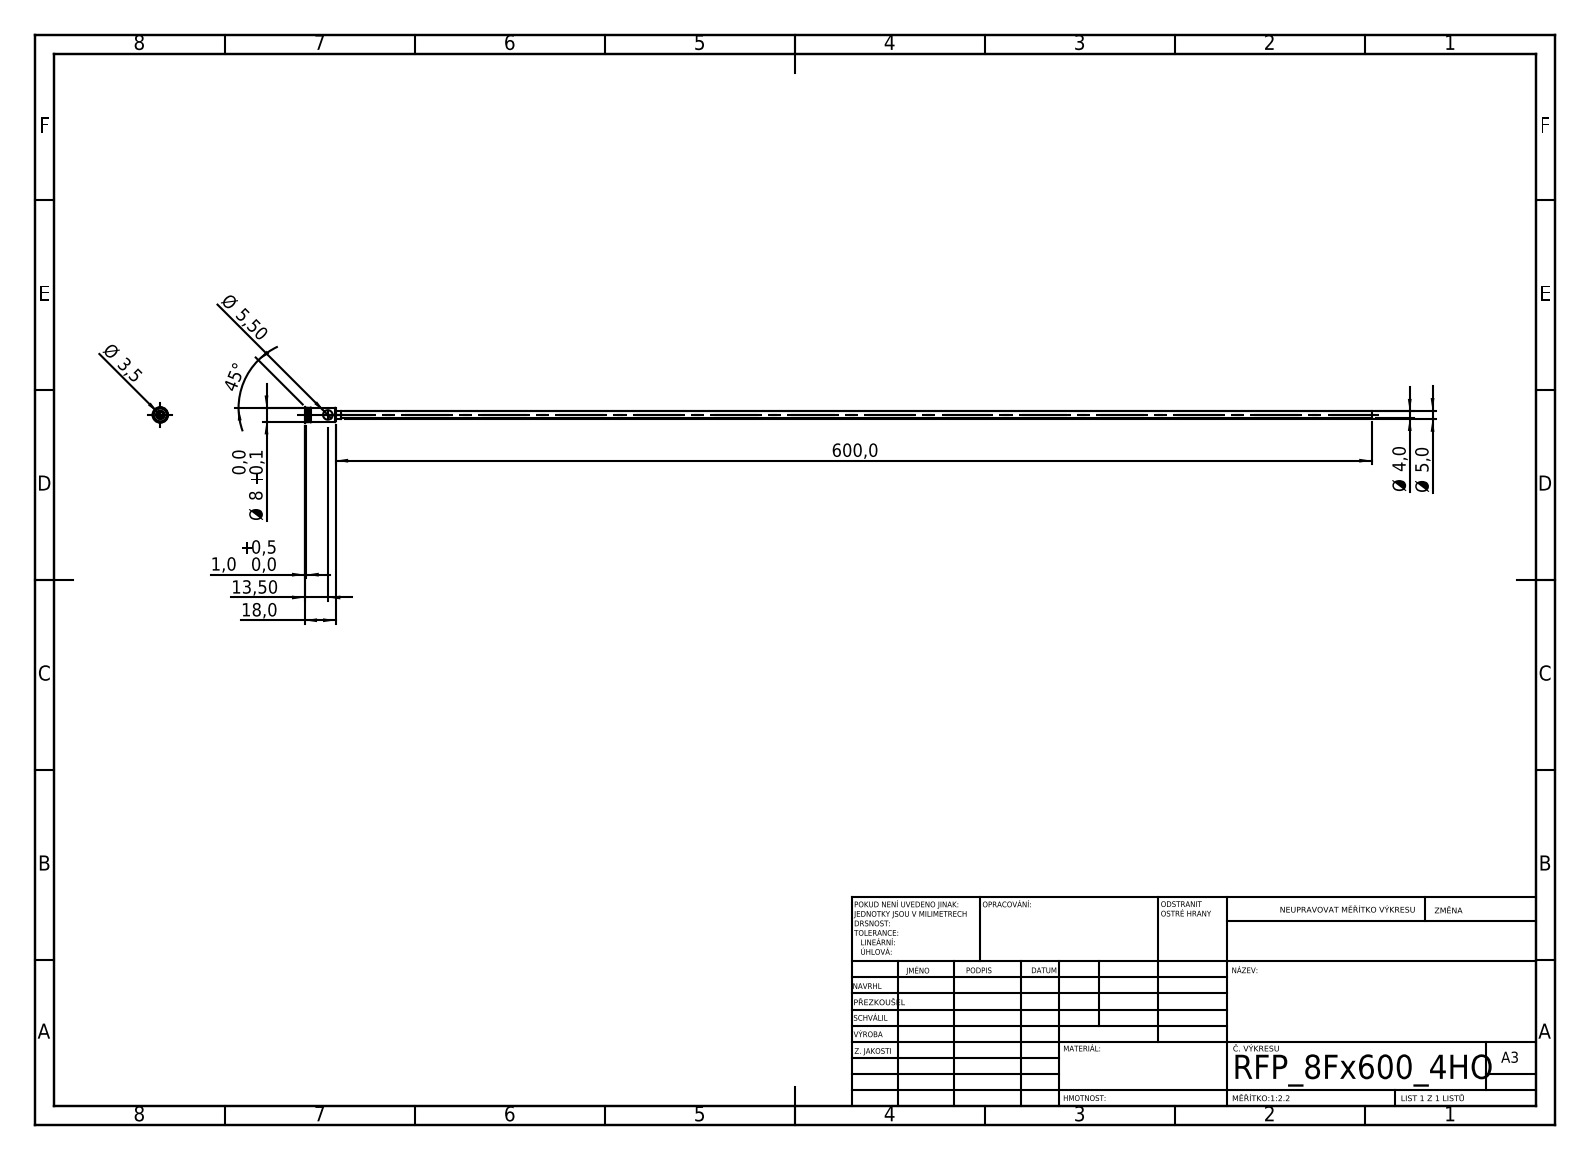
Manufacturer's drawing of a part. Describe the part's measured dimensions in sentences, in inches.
Its 3-D file was written by "SolidWorks 2019 (CONFIG_CONTROL_DESIGN)". It is 1 solid with 44 faces: 20 planar, 16 cylindrical and 8 other. Overall it measures 24.331 by 0.354 by 0.354 inches. Its volume is 0.152 cubic inches and its surface area 22.99 square inches. Round holes: 1 of diameter 0.138, 1 of diameter 0.217. Round bosses or shafts: 1 of diameter 0.354, 1 of diameter 0.315, 1 of diameter 0.197, 1 of diameter 0.157. The main face-to-face distances are 0.709, 0.134, 0.63, 0.079, 0.618, 0.091, 0.118, 0.736, 0.748, 0.827.
